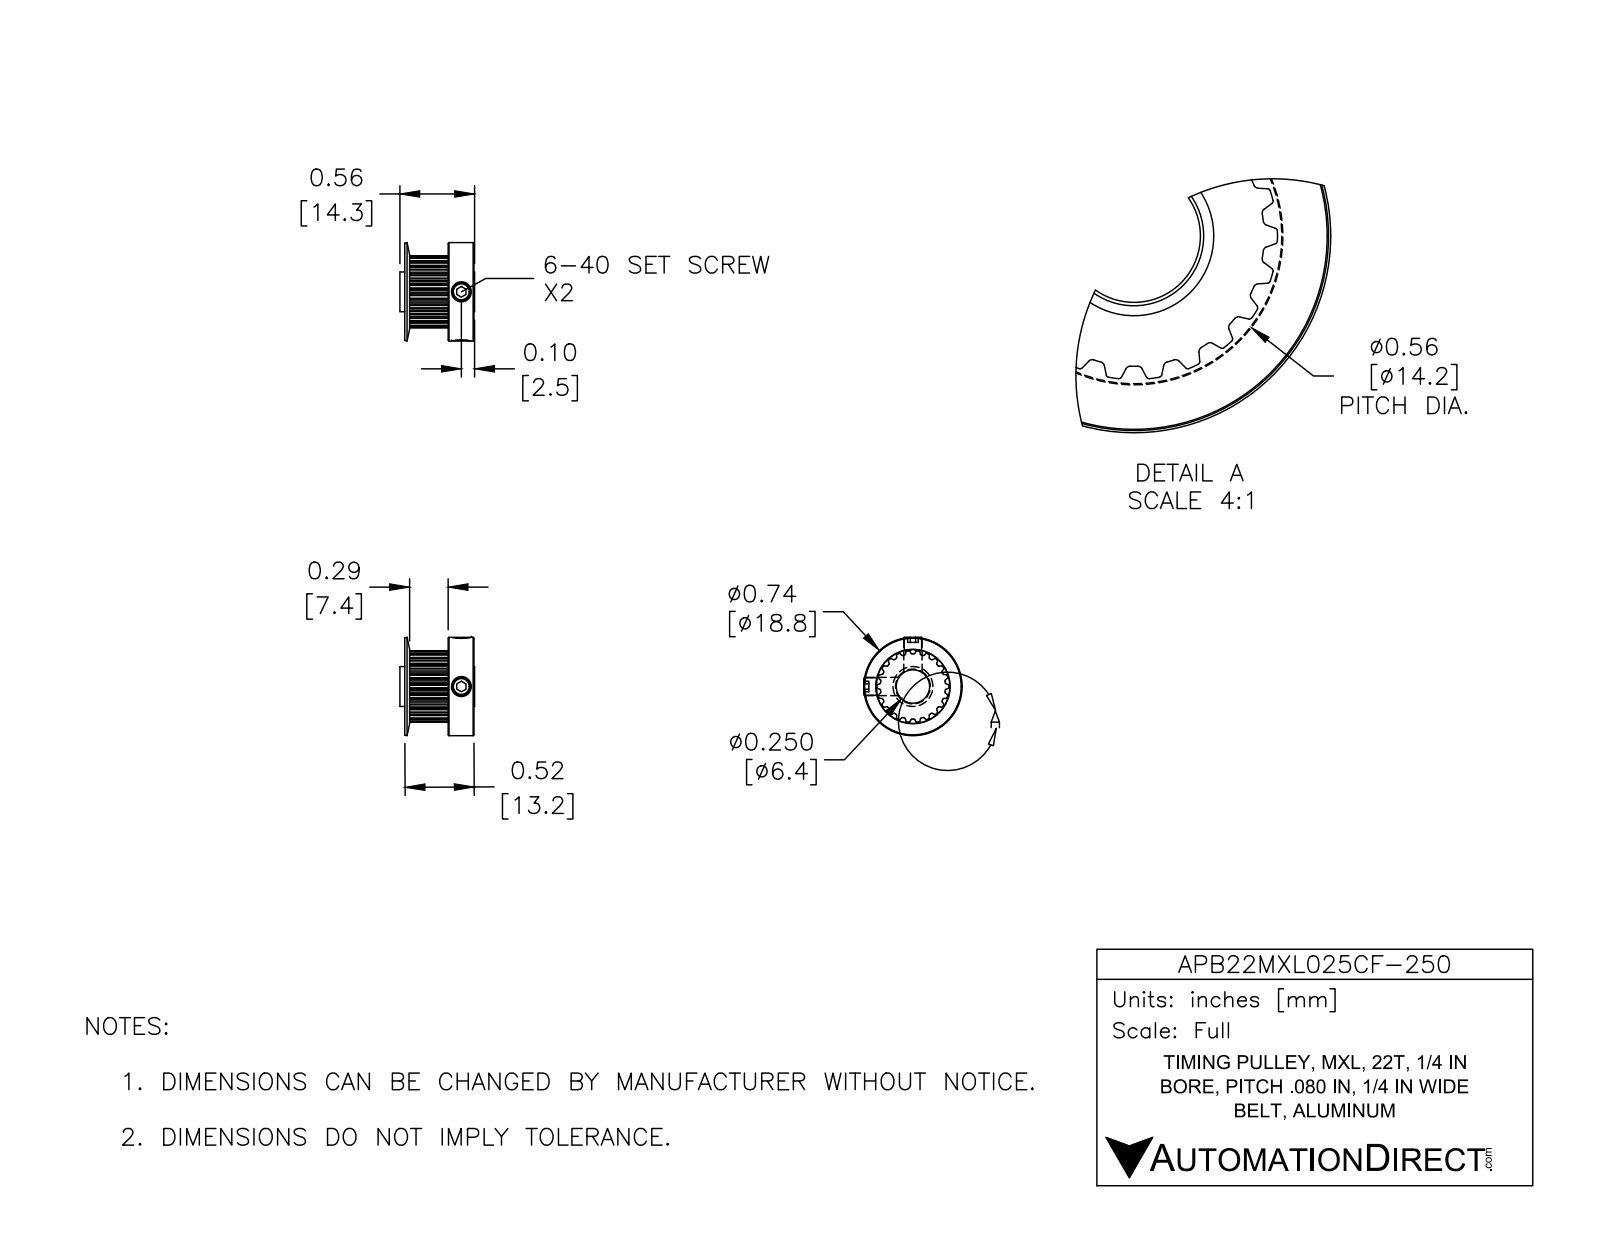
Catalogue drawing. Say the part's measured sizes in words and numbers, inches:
The part is named "APB22MXL025CF-250". Its 3-D file was written by "SolidWorks 2016 (AUTOMOTIVE_DESIGN)". It is 3 solids with 255 faces: 68 planar, 165 cylindrical and 22 other. Overall it measures 0.74 by 0.74 by 0.563 inches. Its volume is 0.123 cubic inches and its surface area 3.125 square inches. Round holes: 2 of diameter 0.138, 1 of diameter 0.25. Round bosses or shafts: 2 of diameter 0.13, 1 of diameter 0.74, 1 of diameter 0.3. Partial cylindrical surfaces (rounded edges, fillets, slot ends): 44 of radius 0.005, 44 of radius 0.009, 1 of radius 0.245, 1 of radius 0.27. The main face-to-face distances are 0.194, 0.309, 0.504, 0.208, 0.019, 0.29, 0.485, 0.508, 0.489, 0.199.
